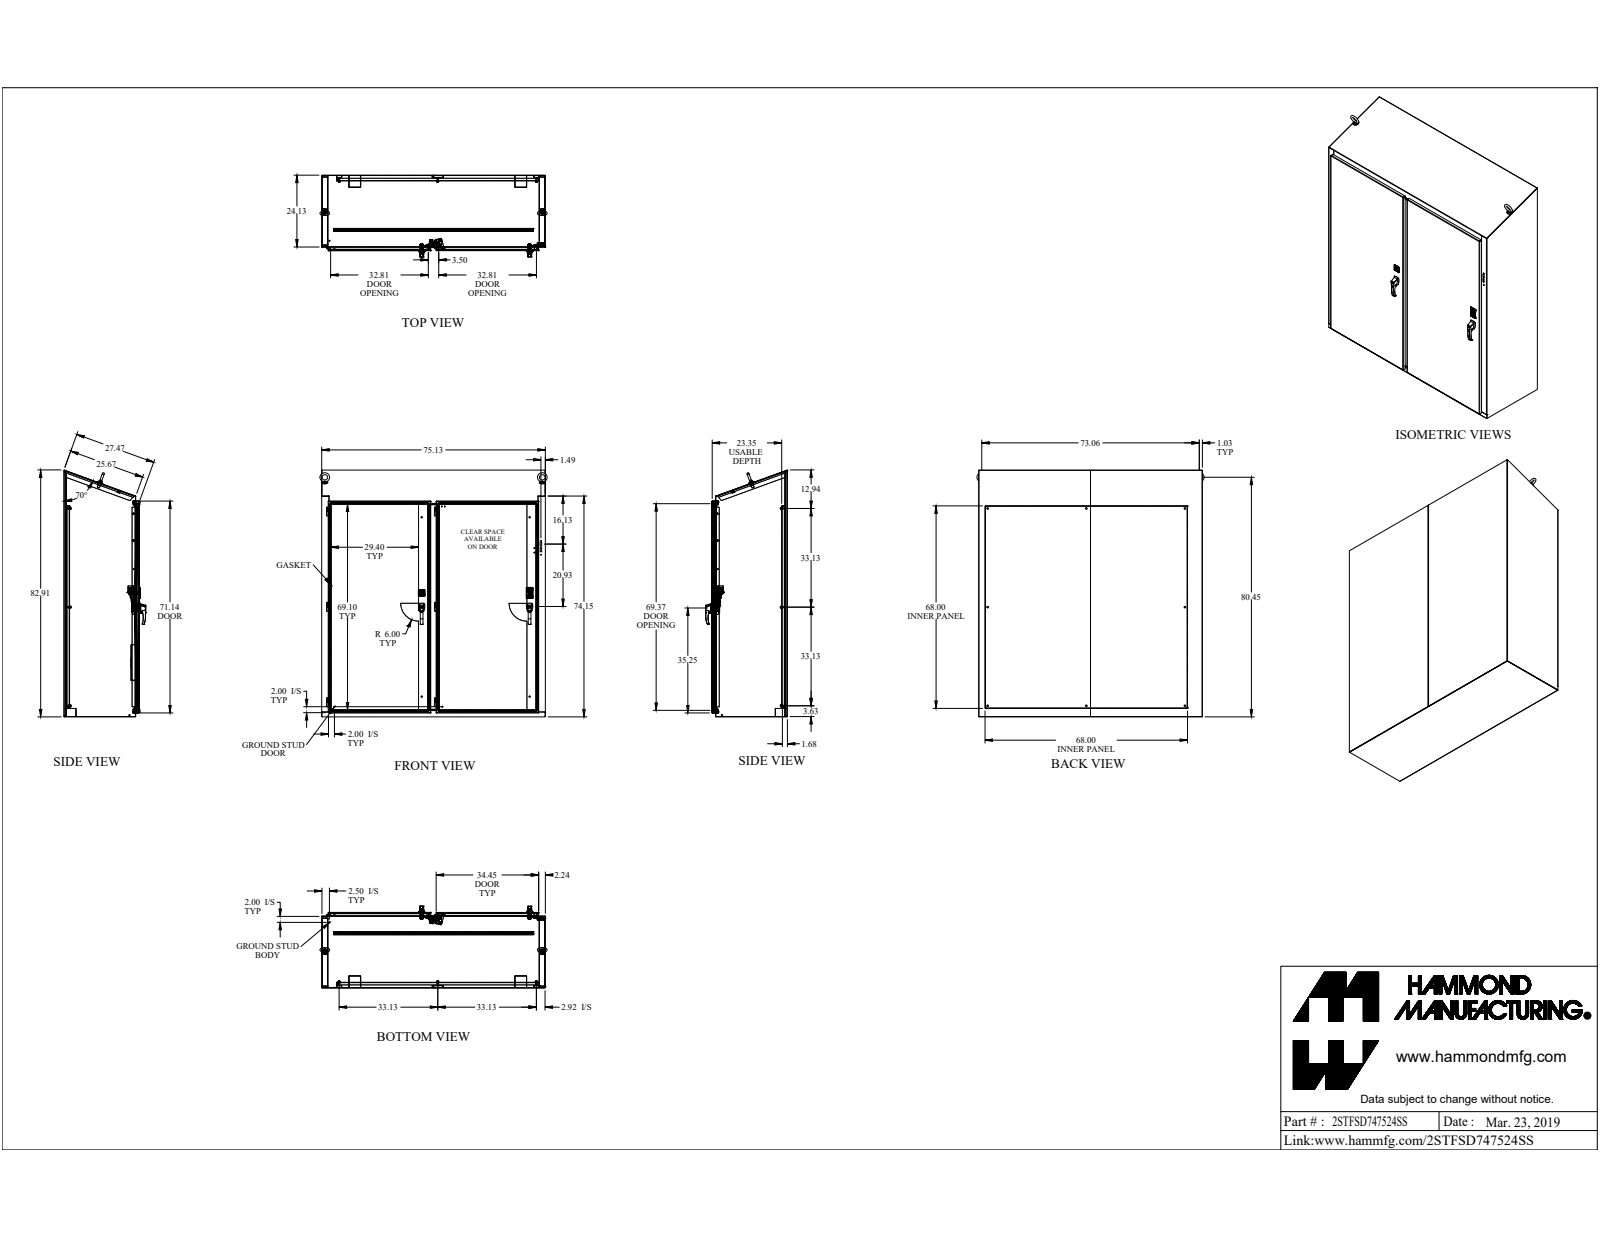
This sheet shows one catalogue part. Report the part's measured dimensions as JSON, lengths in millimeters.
{"part_name": "2STFSD747524SS", "step_written_by": "SolidWorks 2019 (CONFIG_CONTROL_DESIGN)", "units": "millimeters", "bodies": {"solids": 210, "faces": 3274, "planar": 1902, "cylindrical": 992, "other": 380}, "overall_size": [2104.6, 1938.2, 698.3], "volume_mm3": 46640000, "surface_area_mm2": 36700000, "round_holes": [[5, 11], [6.4, 9], [7.1, 9], [7.8, 9], [8.9, 8], [14.3, 8], [6.5, 6], [8, 6], [11.3, 6], [7.1, 4], [7.2, 4], [9.5, 4]], "round_bosses_or_shafts": [[6.4, 18], [25.4, 14], [16.5, 9], [9.5, 9], [15.9, 8], [8.4, 8], [19.1, 6], [12.7, 5]], "partial_cylinders_radius": [[3.2, 64], [1.2, 36], [3.6, 36], [12.7, 34], [0.8, 28], [1.5, 27], [6.4, 24], [0.3, 20]], "face_to_face_distances": [2.4, 2.4, 641.5, 3.2, 46, 48.4, 42.8, 45.3, 1905.8, 0.6], "hole_center_spacings": [1855.7, 1881.4, 1682.8, 841.4, 841.4, 25.4, 920.9, 1189.9]}
